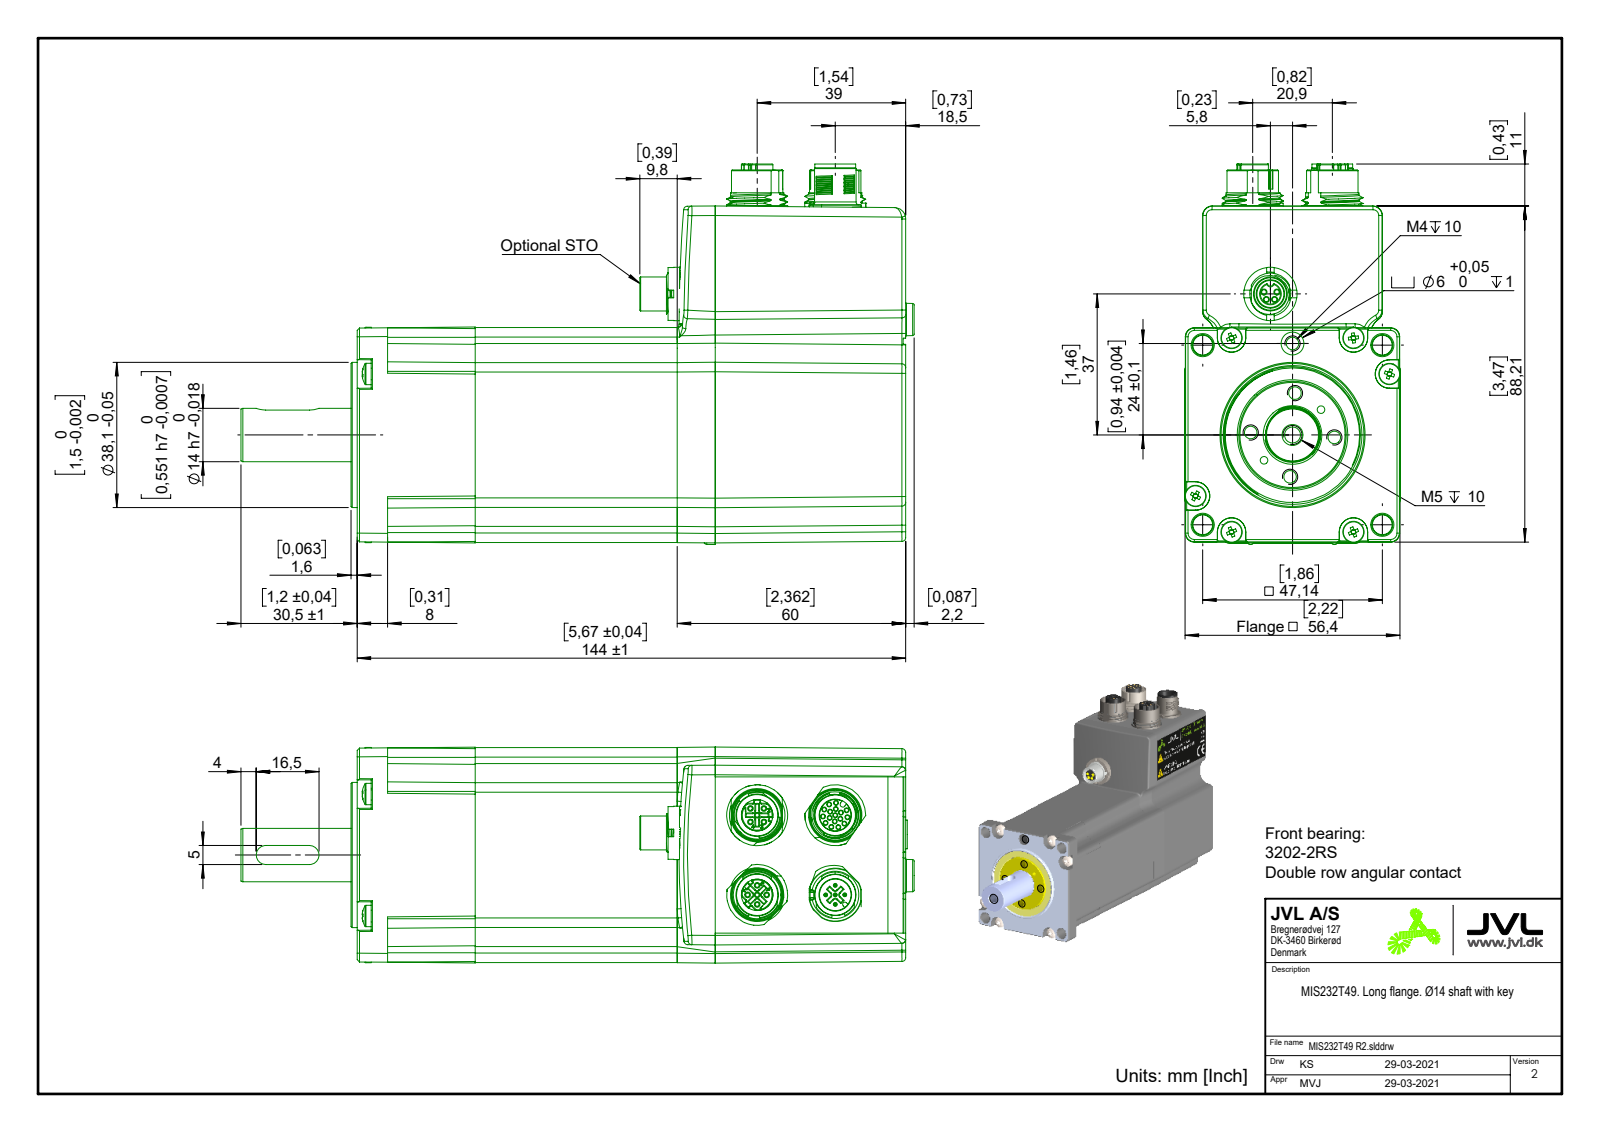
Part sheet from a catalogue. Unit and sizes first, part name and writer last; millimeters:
Units: millimetres
Overall size (bounding box): 176.7 × 99.83 × 56.67
Round holes (diameter × count): ⌀1 ×31, ⌀3.3 ×6, ⌀1.2 ×4, ⌀12.2 ×3, ⌀2 ×2, ⌀11.13 ×2, ⌀4.2 ×1, ⌀6 ×1, ⌀6.76 ×1, ⌀7.1 ×1, ⌀8.3 ×1, ⌀10.9 ×1
Round bosses / shafts (diameter × count): ⌀5.6 ×6, ⌀3 ×6, ⌀1 ×5, ⌀1.6 ×4, ⌀0.8 ×4, ⌀13.5 ×3, ⌀16 ×2, ⌀14 ×2
Partial cylindrical surfaces — rounded edges, fillets, slot ends (radius × count): R0.2 ×54, R2.5 ×31, R0.1 ×20, R0.3 ×16, R1 ×15, R5 ×14, R0.8 ×13, R2.3 ×4
Main face-to-face distances: 56.4, 57.23, 4.75, 52.48, 144, 88.48, 51.92, 0.56, 0.7, 143.3
Hole centre spacings: 3.54, 1.63, 2.5, 3.25, 1.85, 4.94, 1.64, 2.83
Volume: 506 088 mm³ · Surface area: 57 522 mm²
Bodies: 2 solids, 2144 faces (906 planar, 546 cylindrical, 692 other)
Part name (STEP PRODUCT): MIS232T49 R2
STEP written by: SolidWorks 2020 (AUTOMOTIVE_DESIGN)
